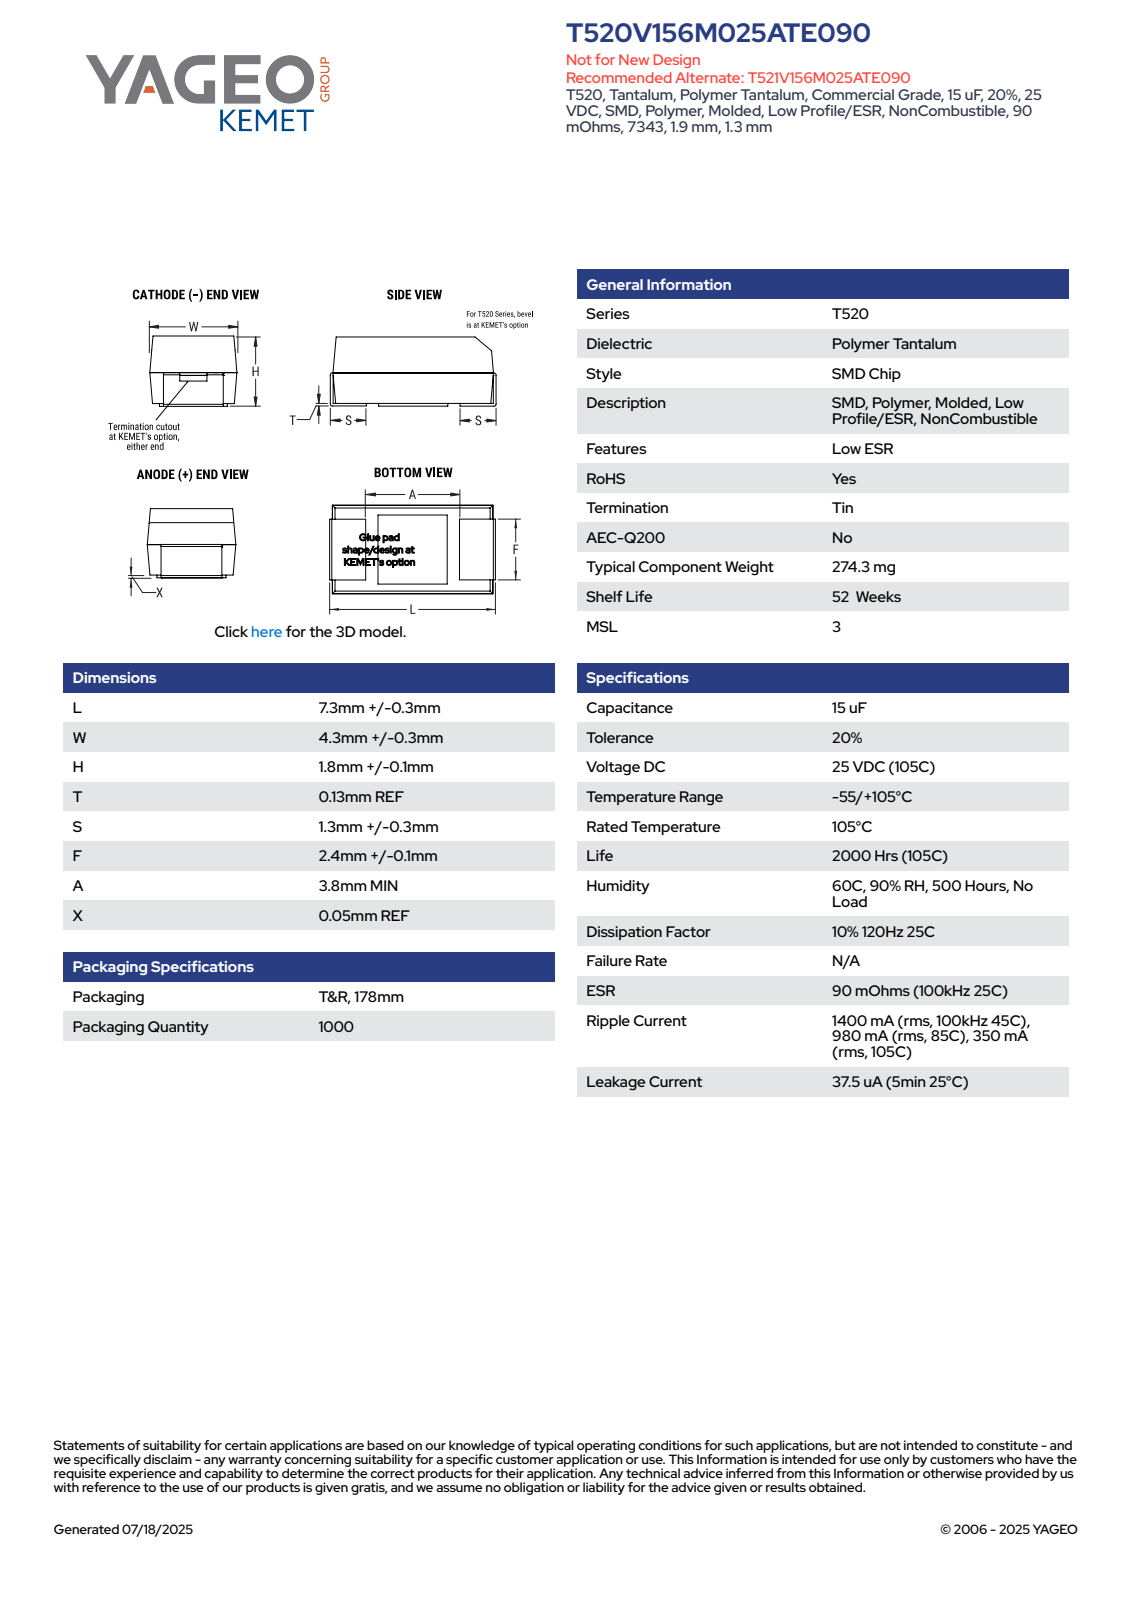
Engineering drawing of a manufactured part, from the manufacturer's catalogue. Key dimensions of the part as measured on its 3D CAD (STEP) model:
Part name (STEP PRODUCT): Case_Anode_14; Case_Top_14; Case_Bottom_14; CTS7343V_L7.6W4.6H1.9S1.3F2.4 (+1 more)
STEP written by: SolidWorks 2014 (AUTOMOTIVE_DESIGN)
Units: millimetres
Bodies: 7 solids, 94 faces (90 planar, 4 cylindrical, 0 other)
Overall size (bounding box): 7.6 × 4.6 × 1.9
Volume: 61 mm³ · Surface area: 199 mm²
Main face-to-face distances: 0.97, 0.8, 1.77, 0.9, 1.87, 4.58, 0.93, 1.9, 7.47, 7.31
